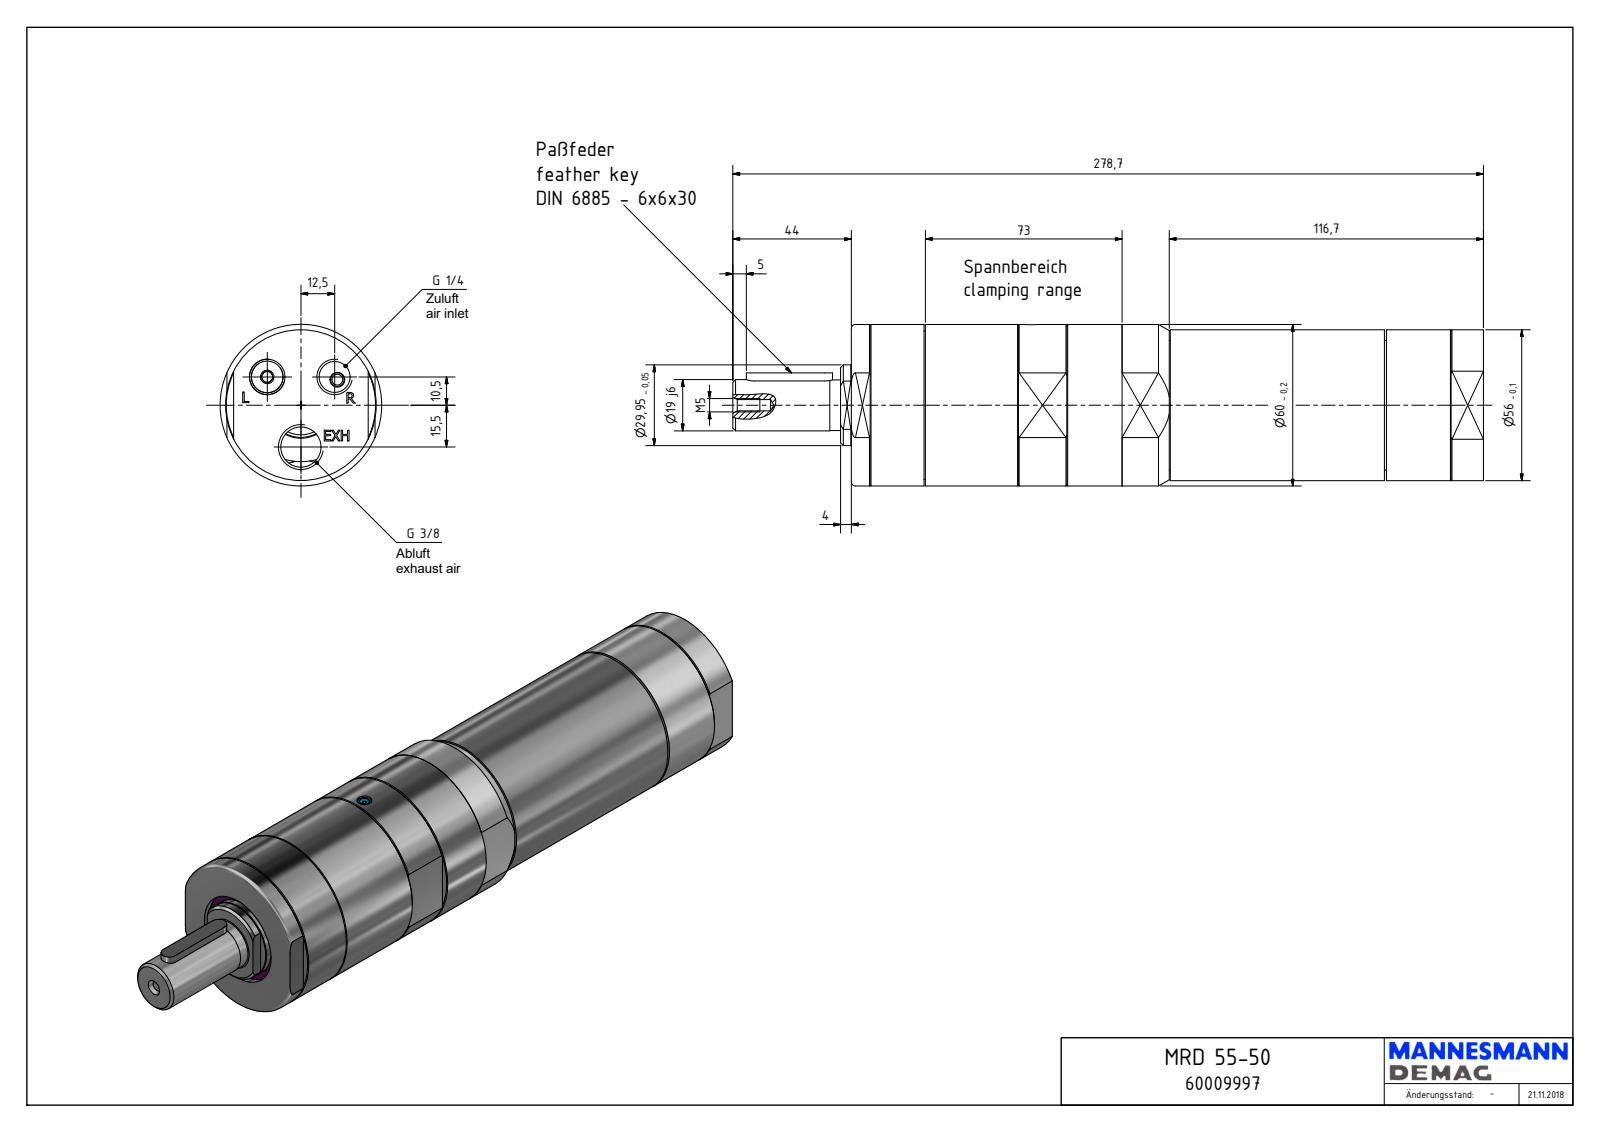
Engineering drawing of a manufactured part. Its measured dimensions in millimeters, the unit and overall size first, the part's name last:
Units: millimetres
Overall size (bounding box): 278.7 × 60 × 60
Round holes (diameter × count): ⌀4 ×2, ⌀1.55 ×1, ⌀4.13 ×1, ⌀5.5 ×1, ⌀11.45 ×1, ⌀14.95 ×1, ⌀35 ×1, ⌀36.5 ×1, ⌀40 ×1, ⌀48.38 ×1, ⌀55.38 ×1
Round bosses / shafts (diameter × count): ⌀60 ×1, ⌀56 ×1, ⌀55.18 ×1, ⌀48.18 ×1, ⌀29.95 ×1, ⌀19 ×1, ⌀18.8 ×1, ⌀5 ×1
Partial cylindrical surfaces — rounded edges, fillets, slot ends (radius × count): R3 ×2, R6 ×2, R5.72 ×1, R19.37 ×1, R23 ×1, R26.95 ×1
Main face-to-face distances: 234.7, 55, 2.5, 52.5, 118.4, 116.3, 197.9, 79.5, 36.8, 0.8
Hole centre spacings: 16.32, 28.85, 15.5, 25
Volume: 624 280 mm³ · Surface area: 59 989 mm²
Bodies: 1 solid, 228 faces (128 planar, 47 cylindrical, 53 other)
Part name (STEP PRODUCT): MRD 55-50_60009997
STEP written by: Autodesk Inventor 2018 (AUTOMOTIVE_DESIGN)
